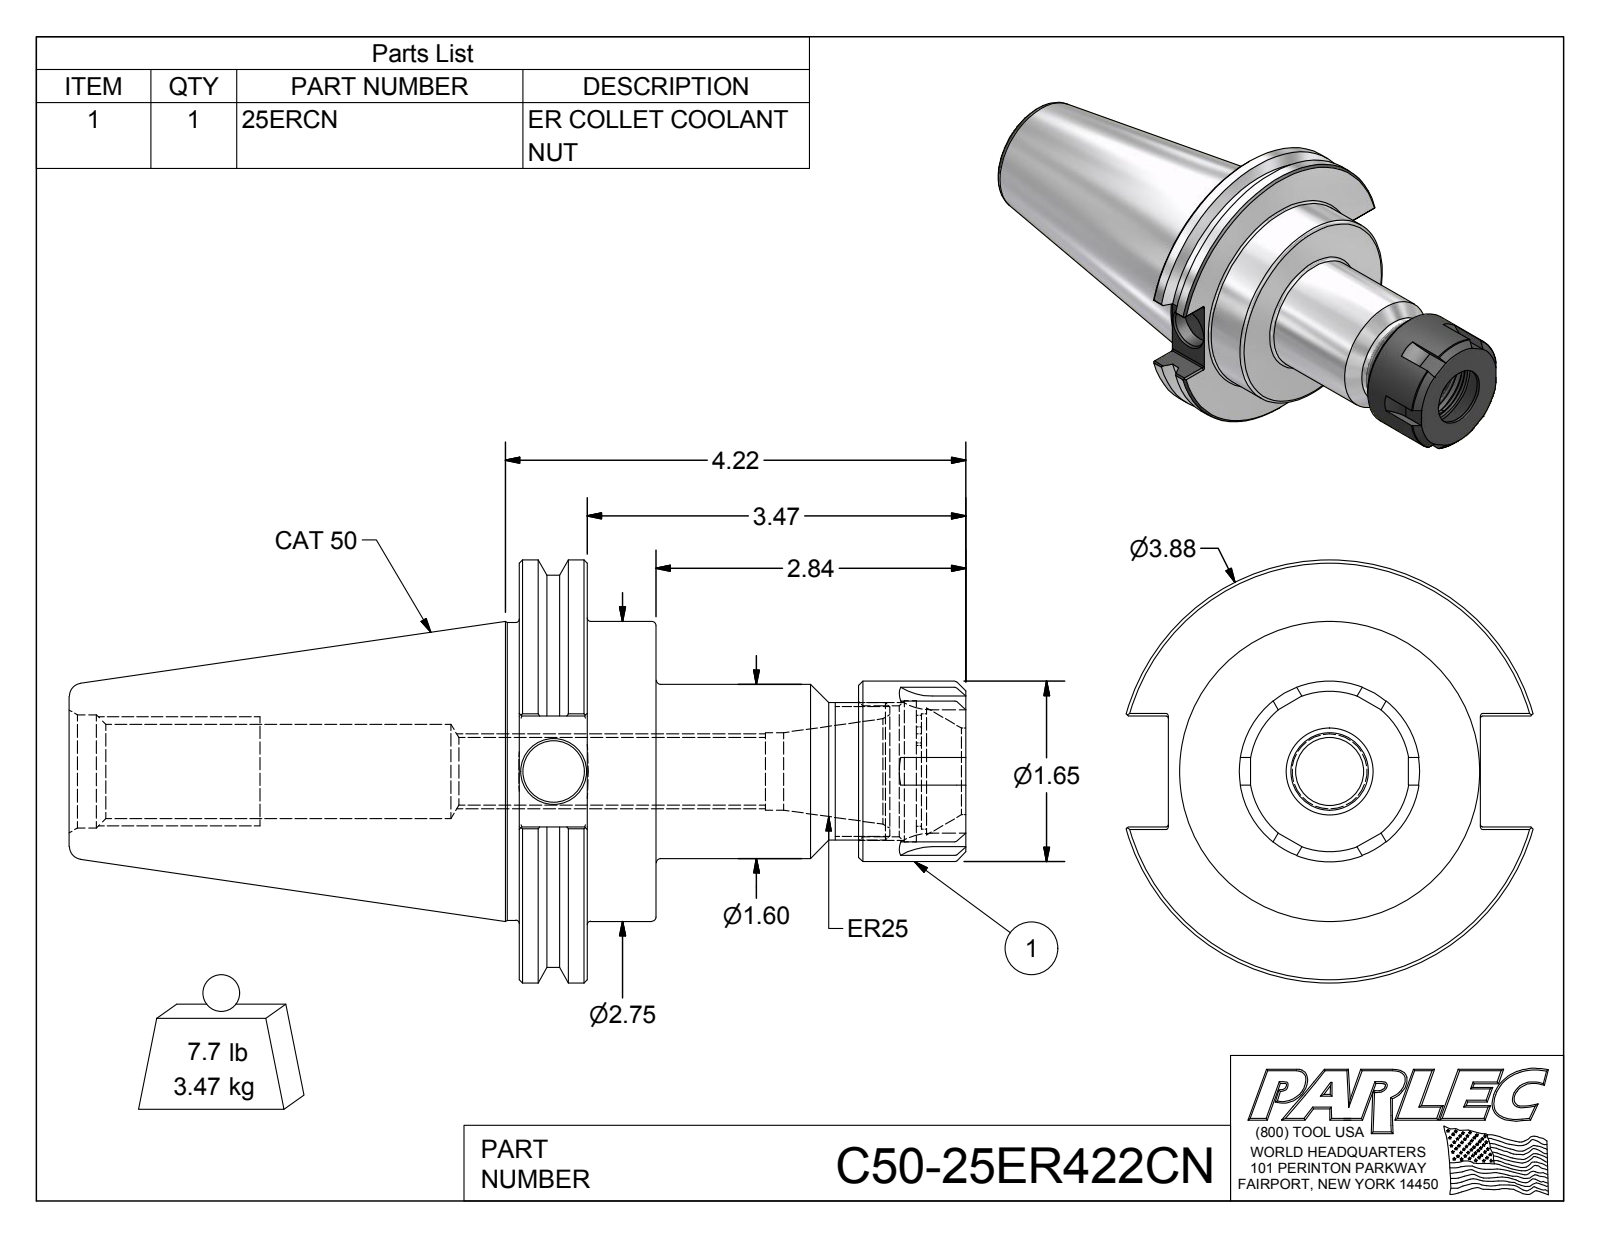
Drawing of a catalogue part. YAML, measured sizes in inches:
part_name: "C50-25ER422CN; C50-25ER4-1; 25ERCN"
step_written_by: "Autodesk Inventor 2012 (AUTOMOTIVE_DESIGN)"
units: inches
bodies: {solids: 2, faces: 139, planar: 56, cylindrical: 43, other: 40}
overall_size: [8.22, 3.875, 3.729]
volume: 27.18
surface_area: 99.66
round_holes:
  - {diameter: 0.563, count: 1}
  - {diameter: 0.62, count: 1}
  - {diameter: 0.71, count: 1}
  - {diameter: 0.794, count: 1}
  - {diameter: 0.865, count: 1}
  - {diameter: 1.038, count: 1}
  - {diameter: 1.057, count: 1}
  - {diameter: 1.201, count: 1}
  - {diameter: 1.294, count: 1}
round_bosses_or_shafts:
  - {diameter: 3.875, count: 1}
  - {diameter: 3.594, count: 1}
  - {diameter: 2.75, count: 1}
  - {diameter: 2.73, count: 1}
  - {diameter: 1.654, count: 1}
  - {diameter: 1.595, count: 1}
  - {diameter: 1.26, count: 1}
partial_cylinders:
  - {radius: 0.02, count: 12}
  - {radius: 0.5, count: 6}
  - {radius: 0.472, count: 1}
  - {radius: 0.515, count: 1}
face_to_face_distances: [0.625, 1.255, 0.63, 4.095, 3.47, 2.84, 3.111, 2.486, 1.856, 0.984]
